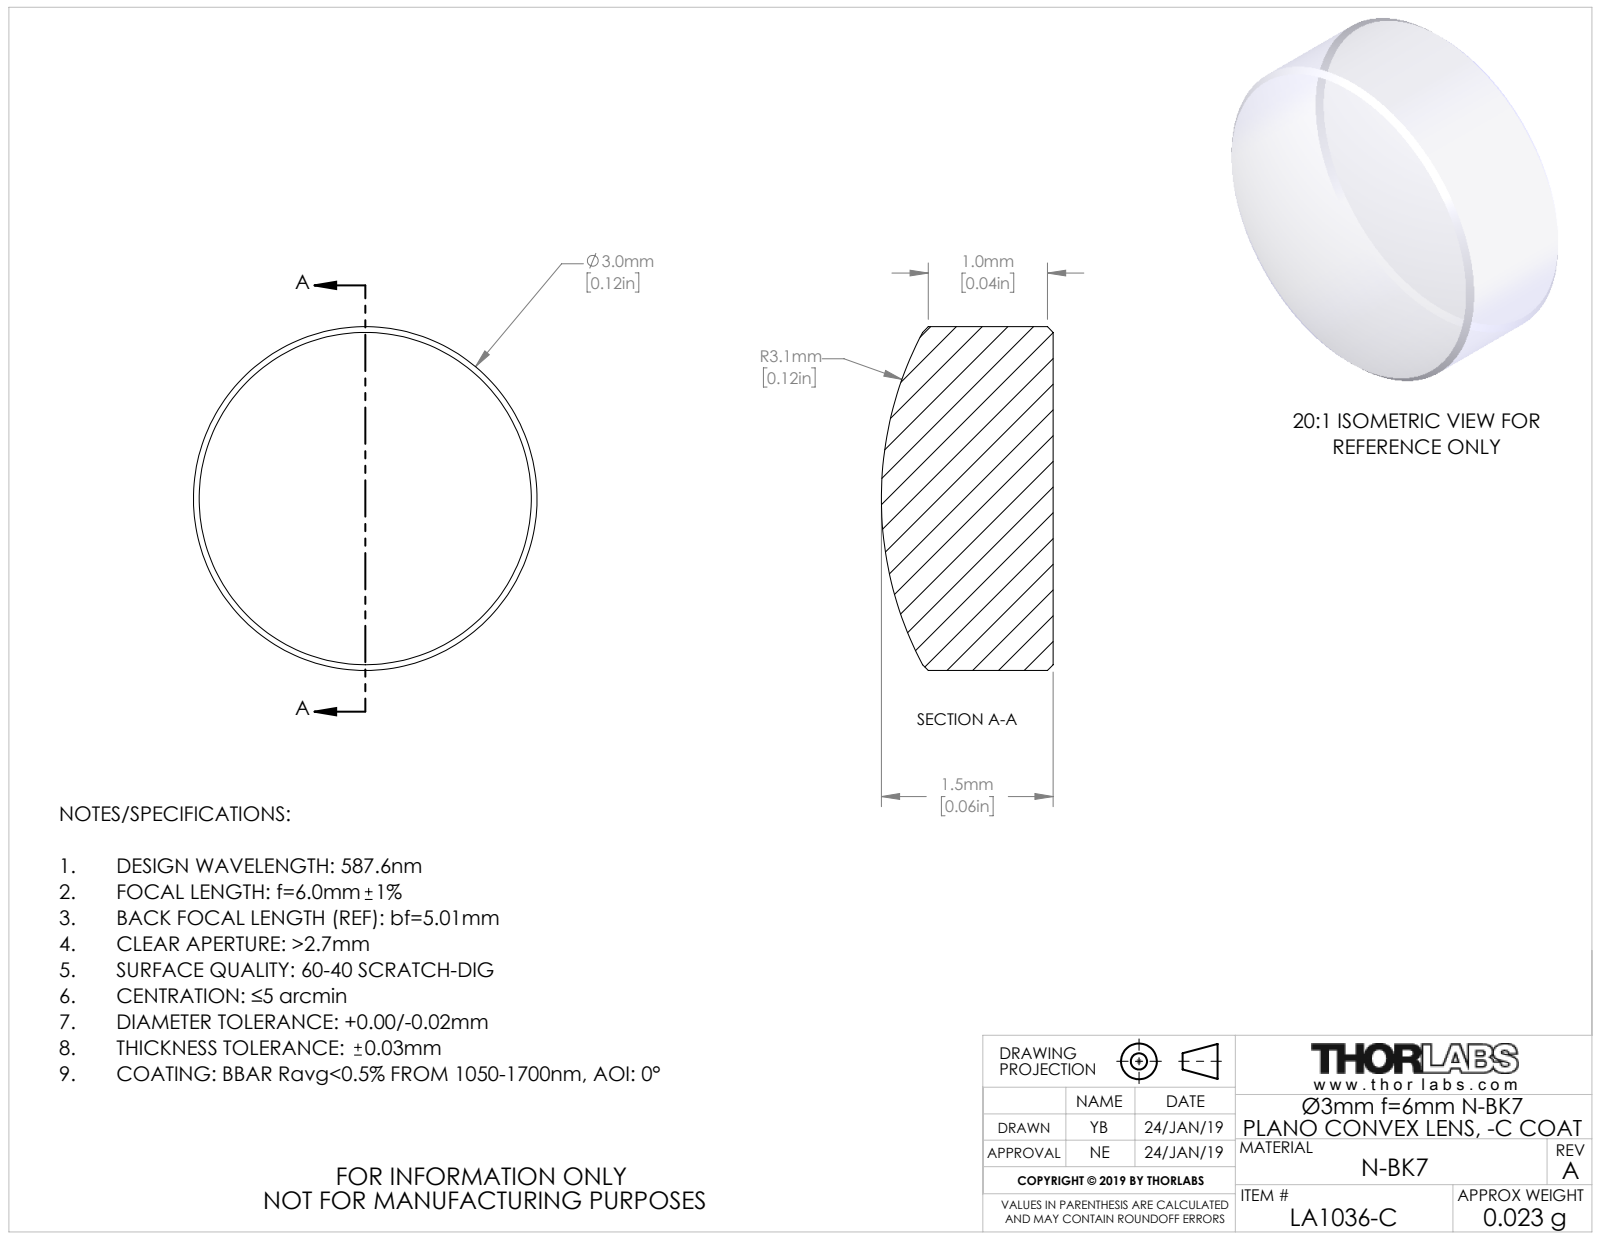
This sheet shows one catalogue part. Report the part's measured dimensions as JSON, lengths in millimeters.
{"part_name": "TTN162614-E0W", "step_written_by": "SolidWorks 2018 (CONFIG_CONTROL_DESIGN)", "units": "millimeters", "bodies": {"solids": 1, "faces": 9, "planar": 1, "cylindrical": 2, "other": 6}, "overall_size": [3, 3, 1.5], "volume_mm3": 9, "surface_area_mm2": 25, "round_bosses_or_shafts": [[3, 1]]}
